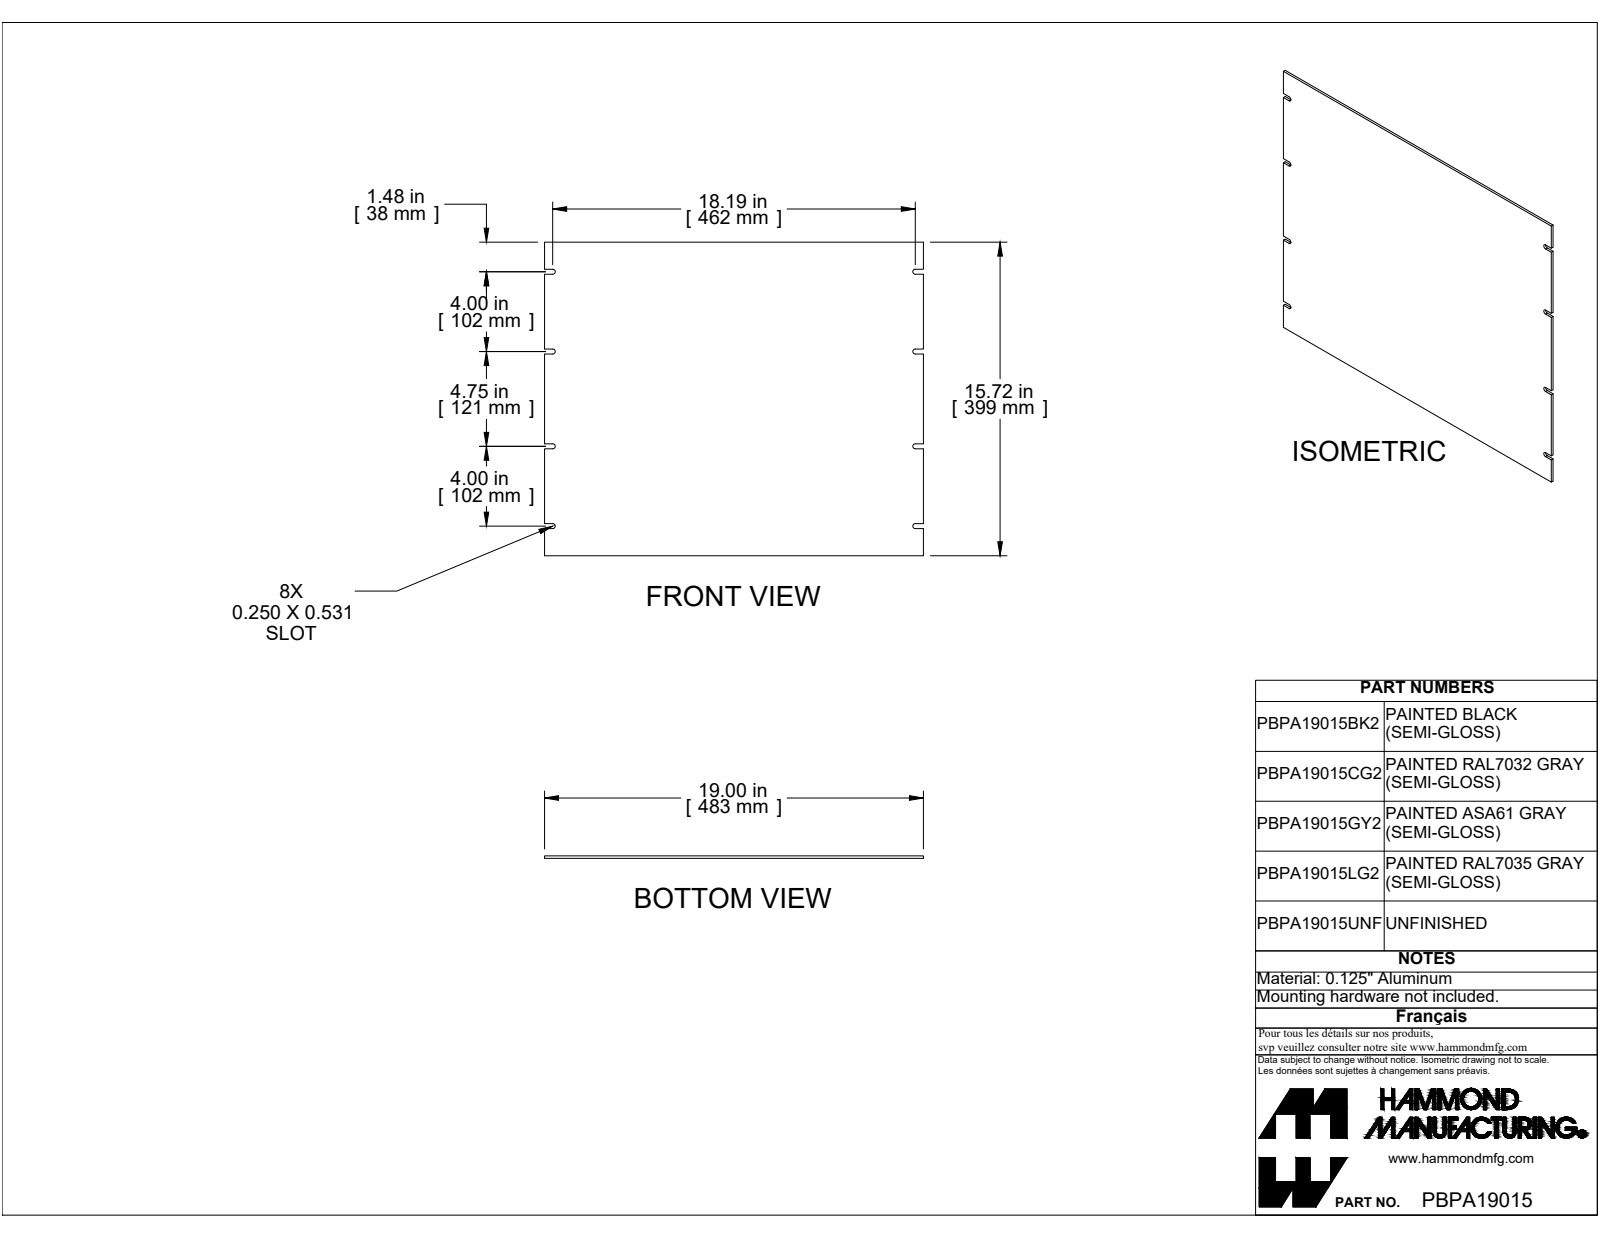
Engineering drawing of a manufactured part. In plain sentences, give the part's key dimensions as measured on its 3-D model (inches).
The part is named "PBPA19015BK2". Its 3-D file was written by "SolidWorks 2019 (CONFIG_CONTROL_DESIGN)". It is 1 solid with 38 faces: 30 planar, 8 cylindrical and 0 other. Overall it measures 19 by 15.718 by 0.125 inches. Its volume is 37.2 cubic inches and its surface area 604.9 square inches. Partial cylindrical surfaces (rounded edges, fillets, slot ends): 8 of radius 0.125. The main face-to-face distances are 0.125, 15.718, 19, 4, 8.75, 0.25, 1.359, 1.609, 5.359, 5.609.
